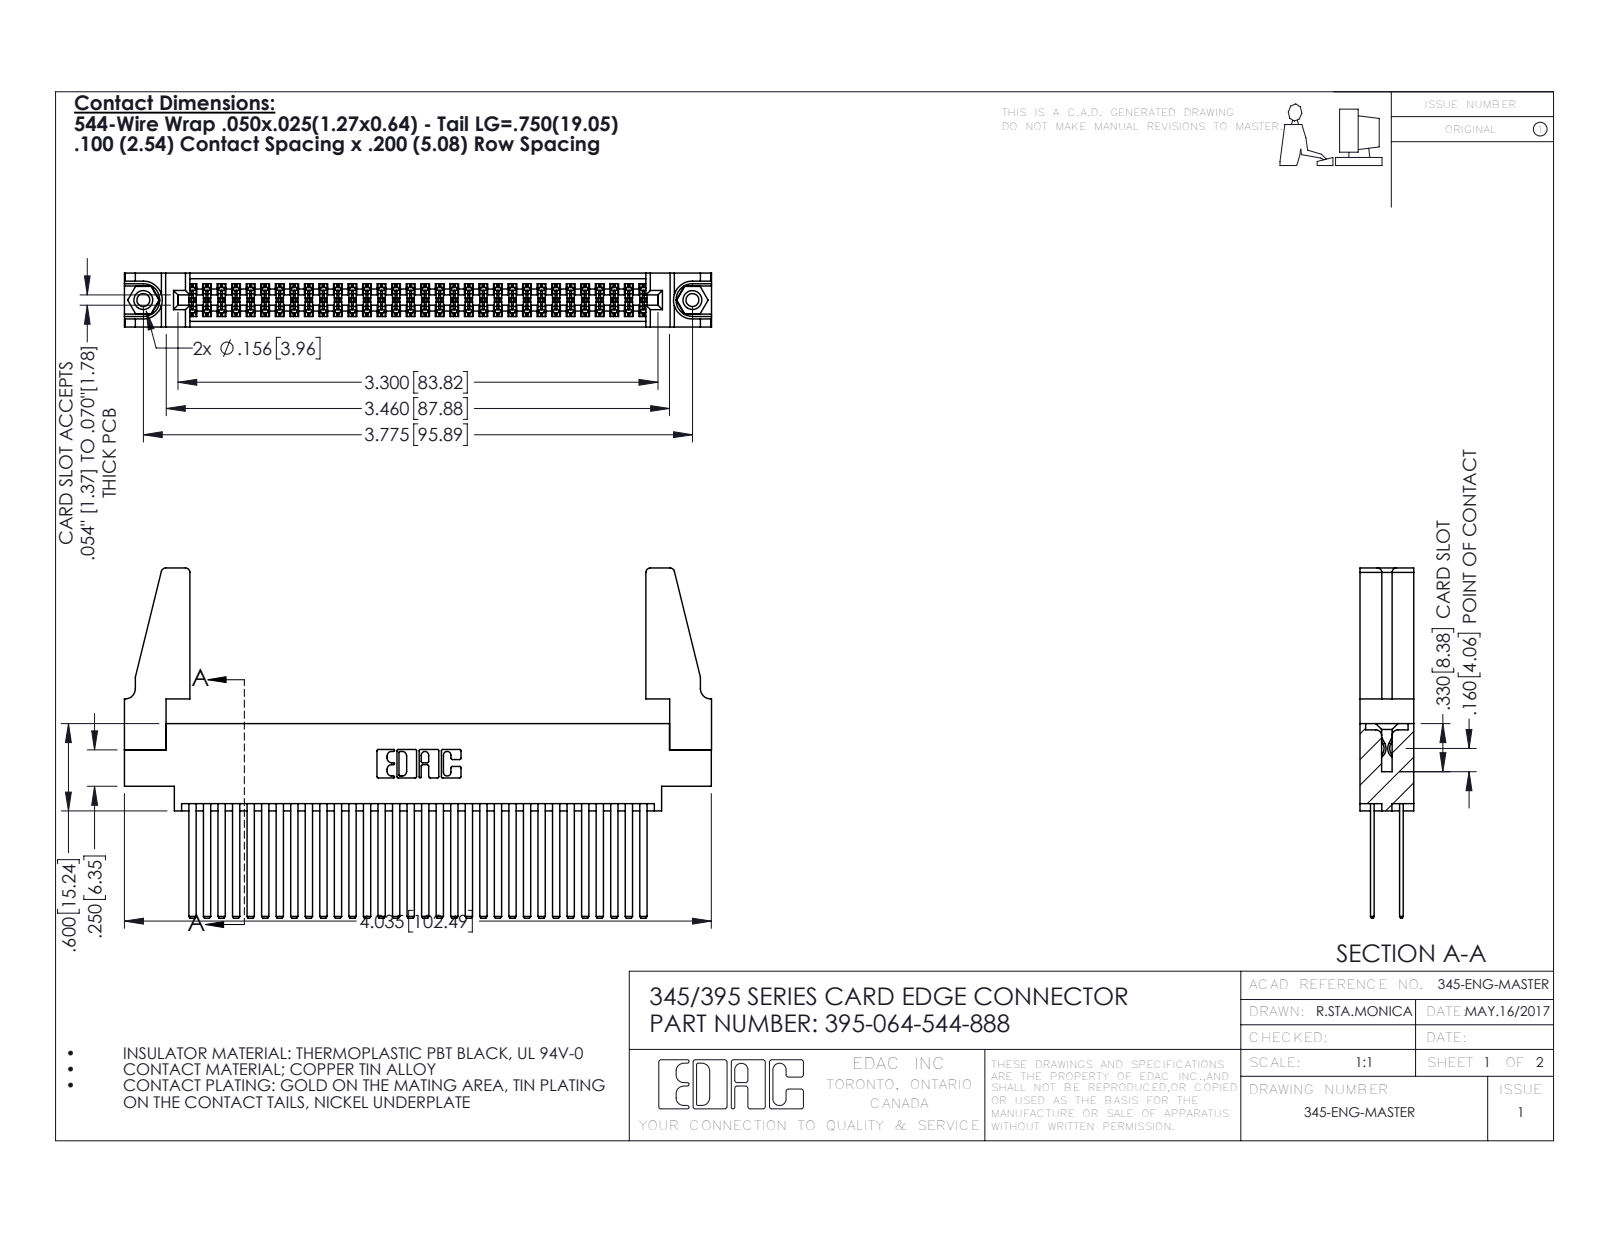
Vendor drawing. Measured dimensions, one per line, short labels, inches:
name: 345-250-001_345-250-001-102; 345-292-001_345-293-144; 345 Part_0.170 Offset - 0.156 Dia-TH; 395-064-544-888 (+1 more)
written by: SolidWorks 2016 (CONFIG_CONTROL_DESIGN)
unit: in
bodies: 69 solids, 3070 faces (2012 planar, 1042 cylindrical, 16 other)
size: 4.036 × 2.407 × 0.37
volume: 0.848 in³; area: 33.24 in²
holes: 2× ⌀0.089, 2× ⌀0.125, 2× ⌀0.156, 1× ⌀0.064
bosses: 2× ⌀0.155
rounds: 96× R0.006, 22× R0.01, 8× R0.03, 6× R0.007, 6× R0.031, 3× R0.026, 2× R0.014, 2× R0.019
face distances: 0.072, 0.298, 0.2, 0.098, 0.272, 0.025, 0.37, 0.225, 0.175, 0.149
hole spacings: 0.27, 3.54, 3.775
